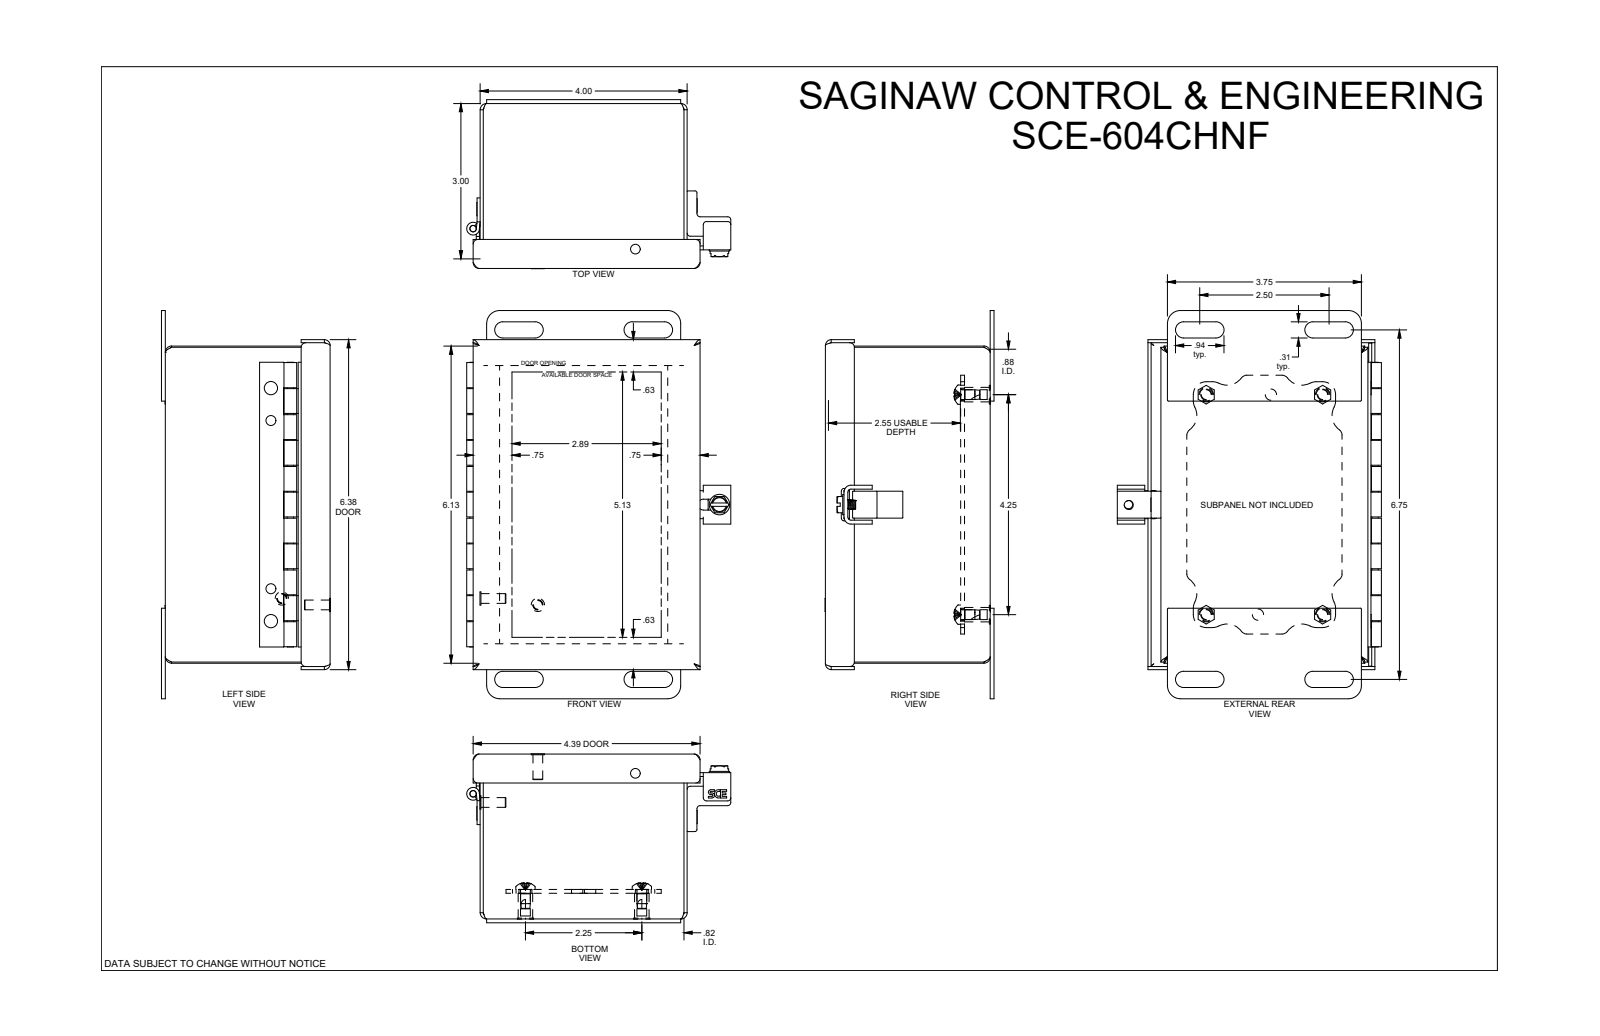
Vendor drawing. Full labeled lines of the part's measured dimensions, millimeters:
Part name (STEP PRODUCT): SCE-604CHNF
STEP written by: SolidWorks 2019 (CONFIG_CONTROL_DESIGN)
Units: millimetres
Bodies: 0 solids, 1004 faces (463 planar, 273 cylindrical, 268 other)
Overall size (bounding box): 190.5 × 129.6 × 82.9
Round holes (diameter × count): ⌀4.8 ×7, ⌀4.9 ×5, ⌀6.4 ×4, ⌀7.1 ×4, ⌀4.9 ×2, ⌀5.5 ×2, ⌀3.2 ×1, ⌀4 ×1, ⌀4.7 ×1, ⌀6.8 ×1
Round bosses / shafts (diameter × count): ⌀4.8 ×10, ⌀6.5 ×5, ⌀9.5 ×4, ⌀7.1 ×4, ⌀10.1 ×1, ⌀6.2 ×1, ⌀3.1 ×1
Partial cylindrical surfaces — rounded edges, fillets, slot ends (radius × count): R0.3 ×50, R6.4 ×16, R1.5 ×13, R1.3 ×8, R2.8 ×8, R3.2 ×8, R4 ×8, R8.7 ×8
Main face-to-face distances: 1.5, 79.4, 100.1, 80.9, 77.9, 154.1, 101.6, 1.9, 98.6, 1.9
Hole centre spacings: 57.2, 57.2, 108, 109.5, 110.9, 122.1, 7.1, 7.7
